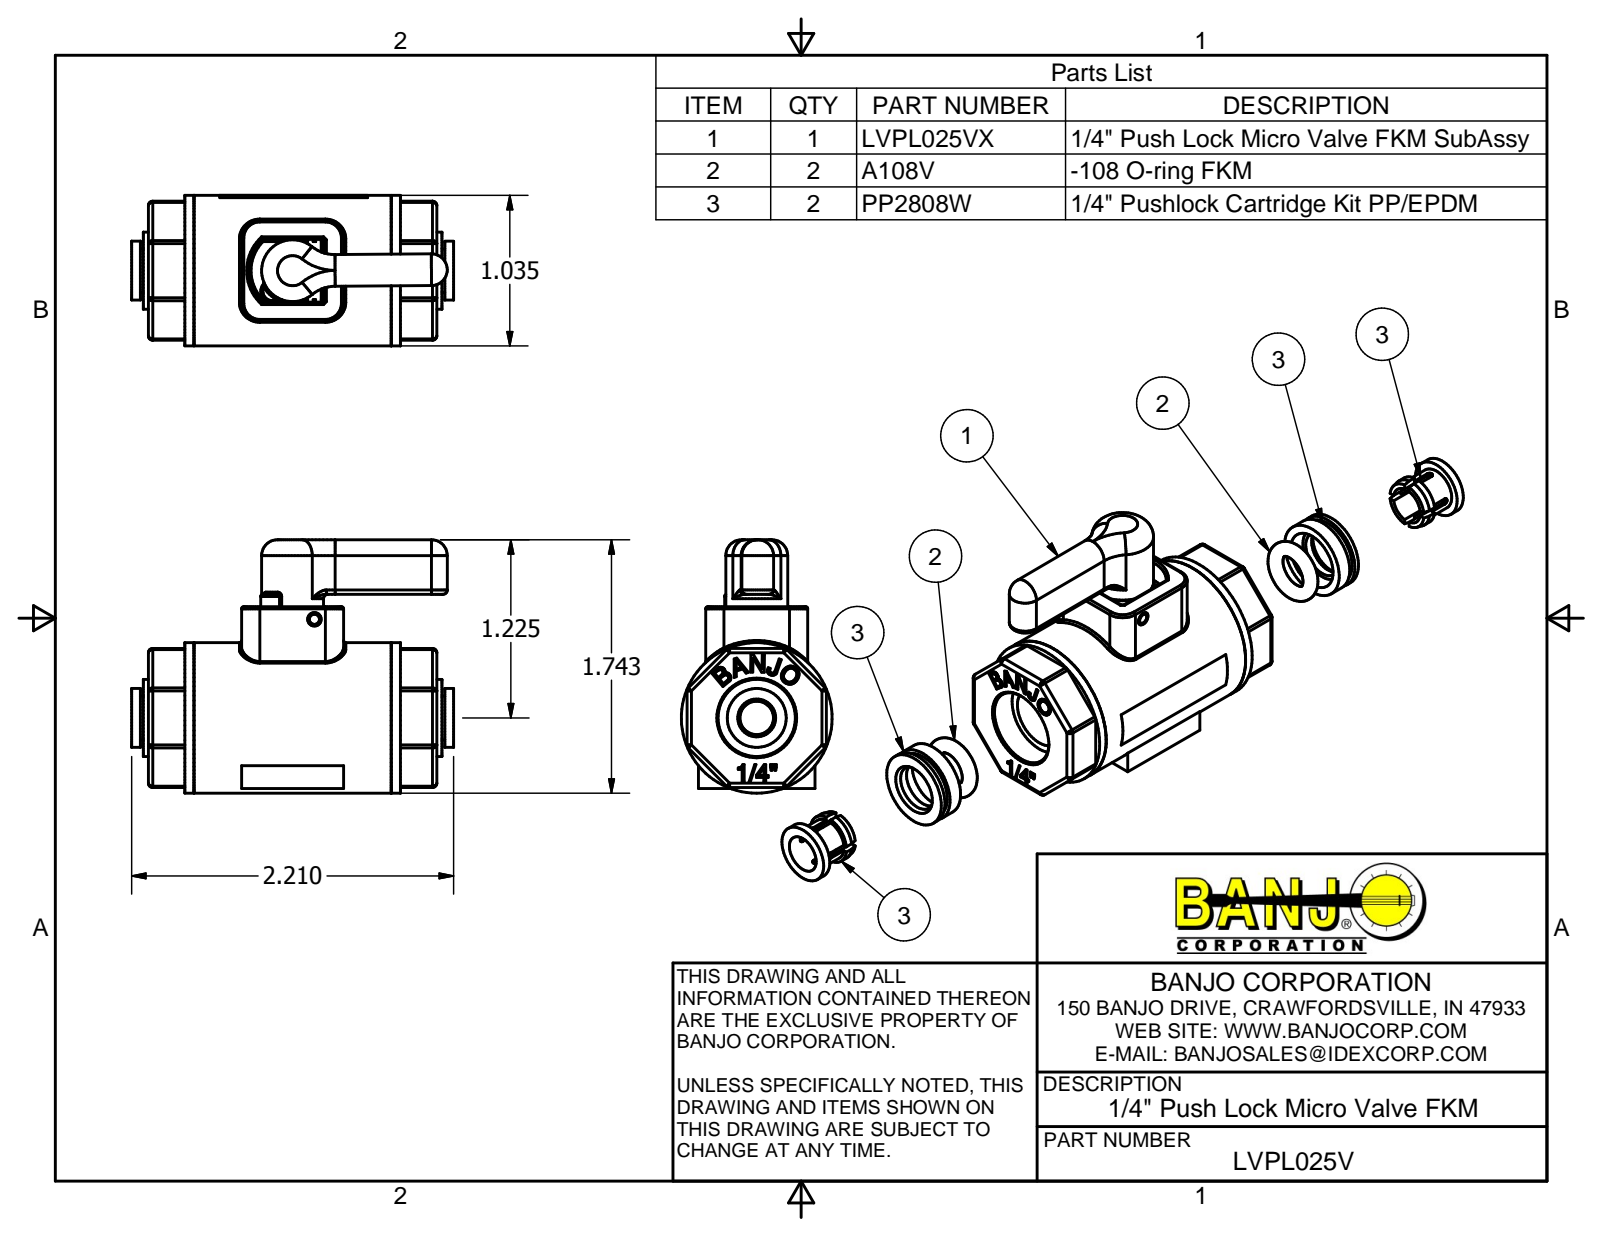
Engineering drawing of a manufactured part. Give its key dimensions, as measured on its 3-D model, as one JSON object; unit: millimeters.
{"part_name": "LV03254A; AQ010V; LV02153B; LEV03255 (+8 more)", "step_written_by": "Autodesk Inventor 2014 (AUTOMOTIVE_DESIGN)", "units": "millimeters", "bodies": {"solids": 18, "faces": 781, "planar": 360, "cylindrical": 173, "other": 248}, "overall_size": [56.13, 44.26, 26.29], "volume_mm3": 27775, "surface_area_mm2": 20132, "round_holes": [[2.36, 1], [5.84, 1], [6.38, 1], [6.48, 1], [6.6, 1], [8.13, 1], [9.3, 1], [9.4, 1], [9.55, 1], [10.69, 1], [10.77, 1], [13.41, 1]], "round_bosses_or_shafts": [[26.29, 1], [21.46, 1], [20.62, 1], [19.94, 1], [13.46, 1], [12.06, 1], [10.79, 1], [10.29, 1]], "partial_cylinders_radius": [[0.76, 26], [0.25, 16], [0.38, 14], [0.57, 4], [3.17, 4], [1.27, 2], [2.77, 2], [6.35, 2]], "face_to_face_distances": [24.82, 9.58, 7.95, 17.53, 32.77, 42.35, 1.27, 24.28, 15.24, 8.31]}
